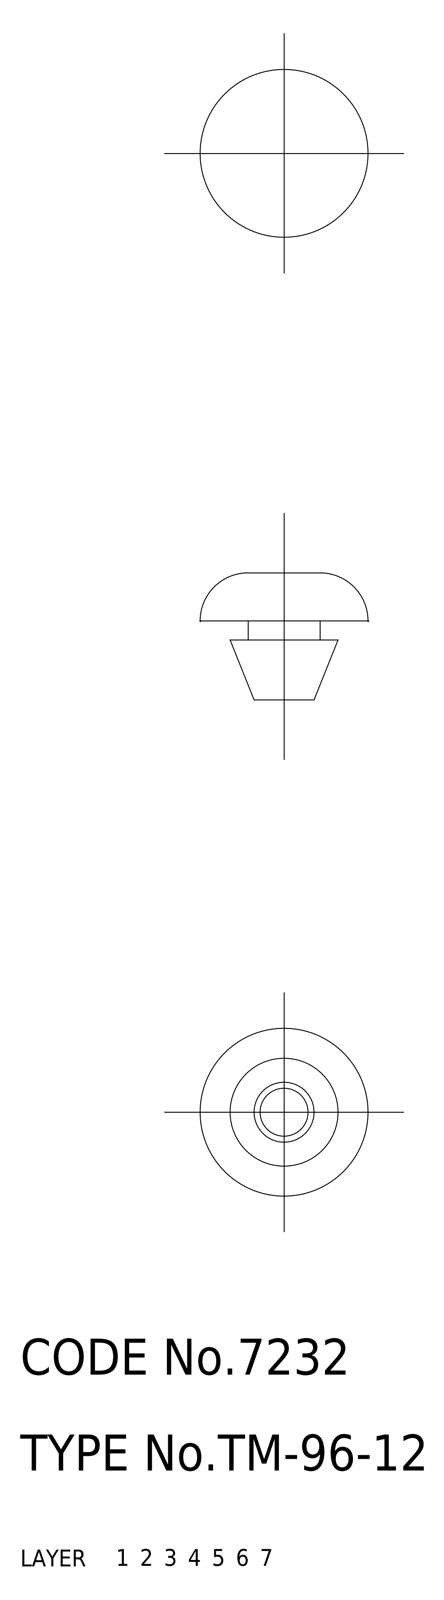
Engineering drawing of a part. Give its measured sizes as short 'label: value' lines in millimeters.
name: cushion
written by: CADfix (AUTOMOTIVE_DESIGN)
unit: mm
bodies: 1 solid, 13 faces (0 planar, 0 cylindrical, 13 other)
size: 14 × 14 × 10.6
volume: 645 mm³; area: 660 mm²
